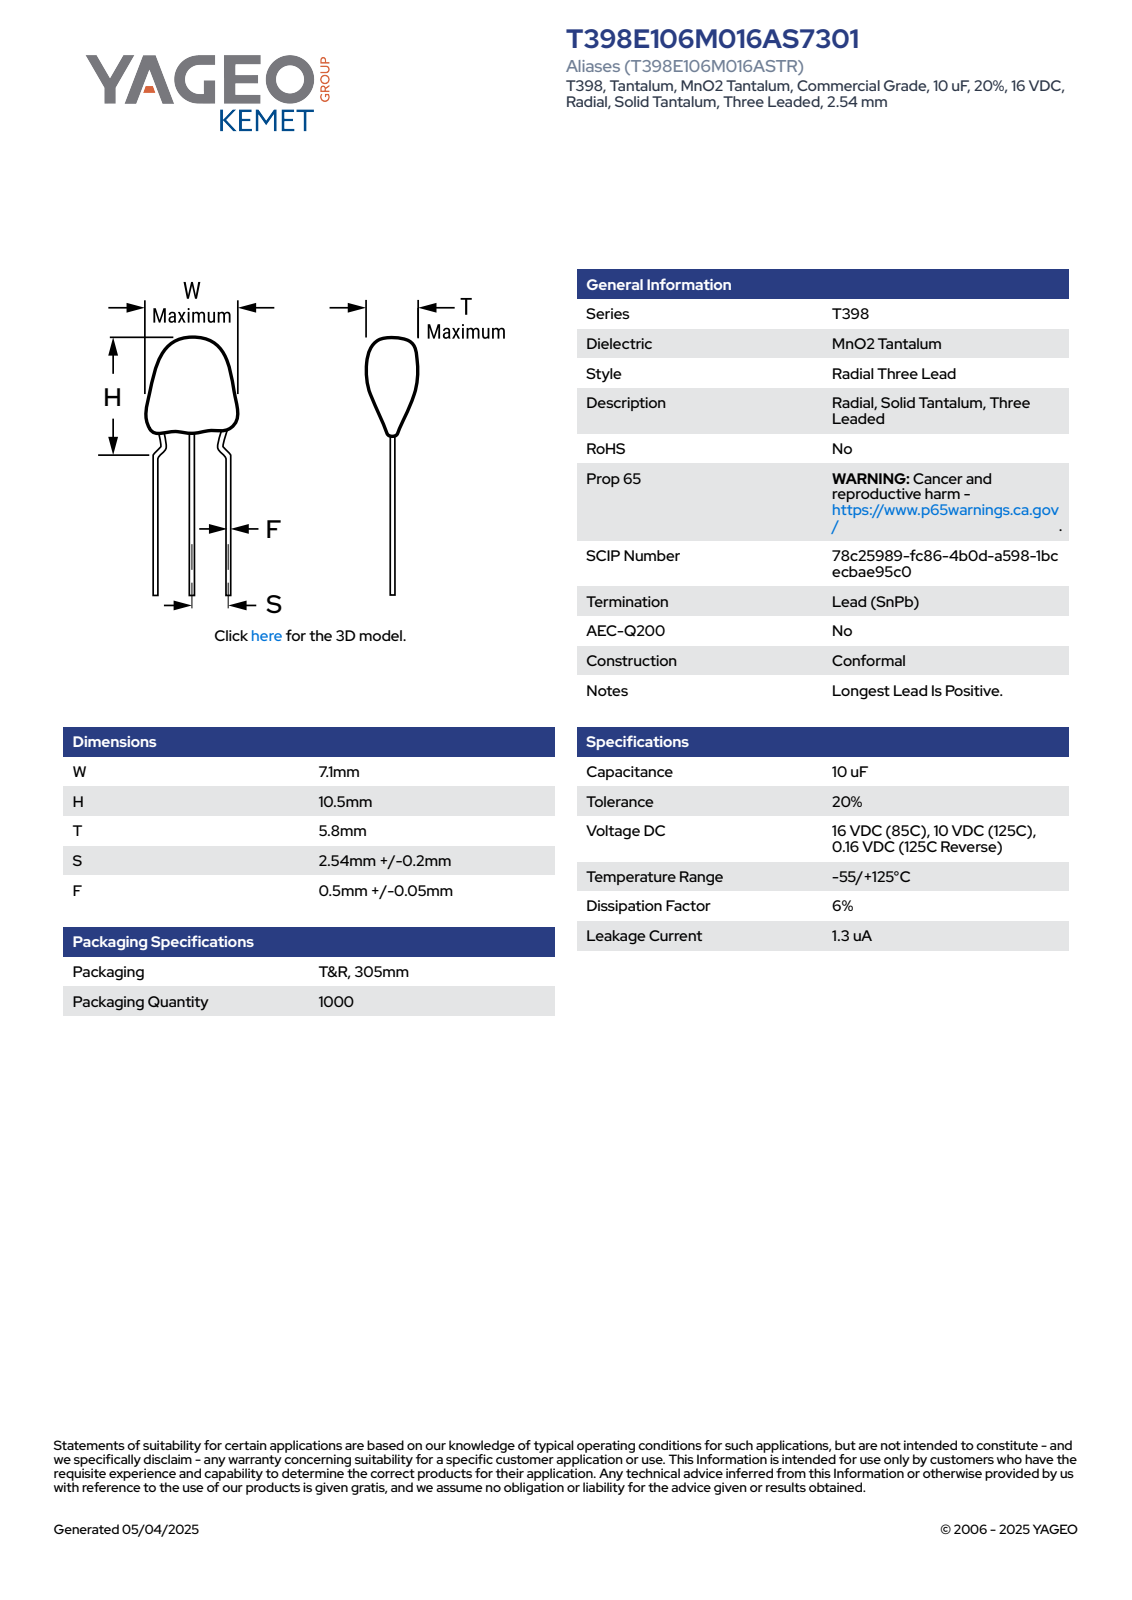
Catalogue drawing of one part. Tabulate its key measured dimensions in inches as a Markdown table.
| quantity | value |
| --- | --- |
| part name | CTR_T398_W7.1H10.5T5.8S2.54LL6.02F0.55 |
| STEP written by | SolidWorks 2014 (AUTOMOTIVE_DESIGN) |
| units | inches |
| bodies | 4 solids, 91 faces (67 planar, 8 cylindrical, 16 other) |
| overall size | 0.65 × 0.28 × 0.189 |
| volume | 0.017 in³ |
| surface area | 0.423 in² |
| round bosses / shafts (diameter × count) | 0.022 × 3 |
| partial cylindrical surfaces (radius × count) | 0.197 × 2 |
| main face-to-face distances | 0.189, 0.28, 0.288, 0.036, 0.504, 0.216, 0.468, 0.18, 0.013, 0.074 |
